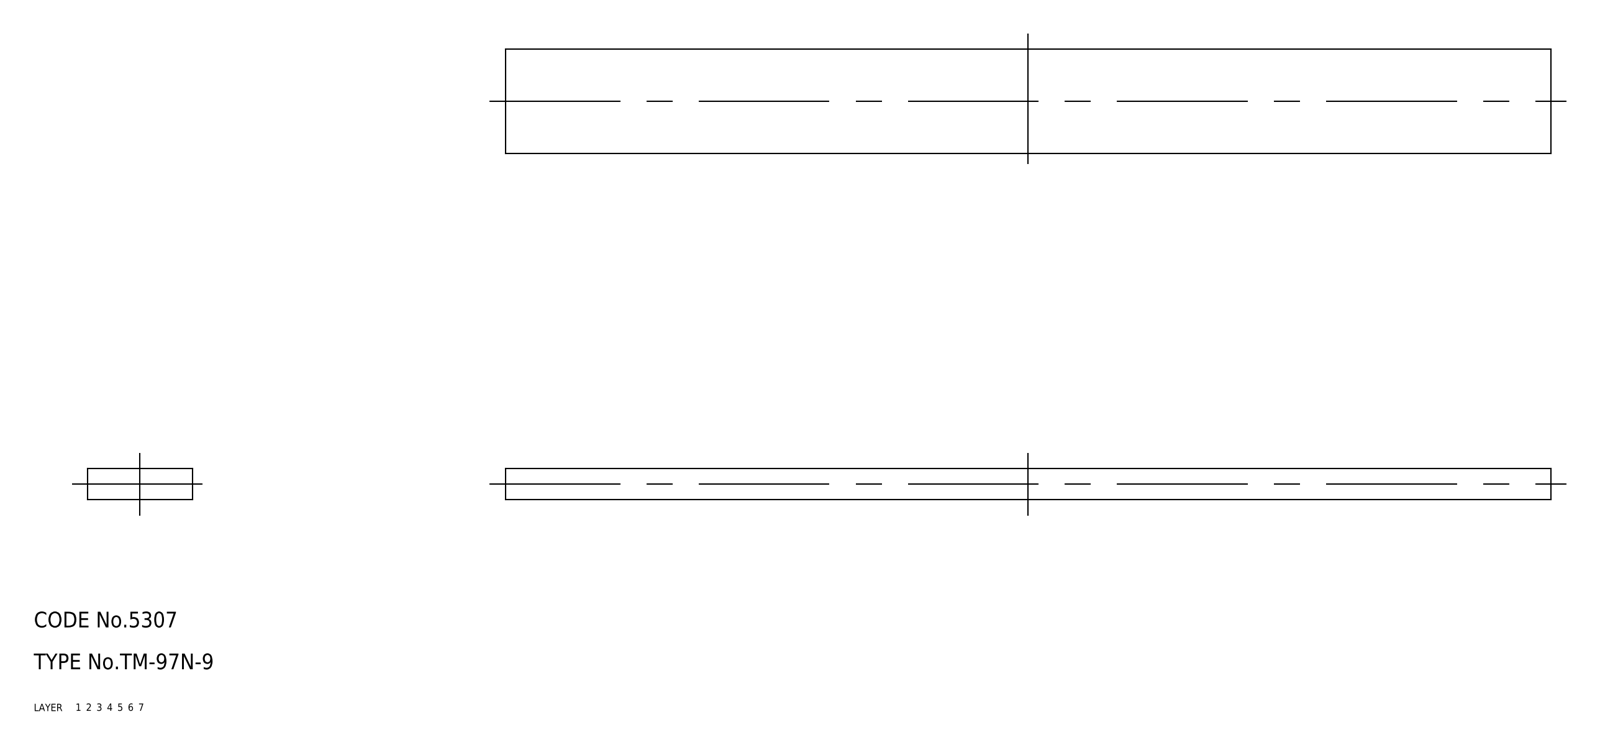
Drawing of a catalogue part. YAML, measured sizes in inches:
part_name: "rubber foam"
step_written_by: "CADfix (AUTOMOTIVE_DESIGN)"
units: inches
bodies: {solids: 1, faces: 6, planar: 0, cylindrical: 0, other: 6}
overall_size: [7.874, 0.787, 0.236]
volume: 1.465
surface_area: 16.49
